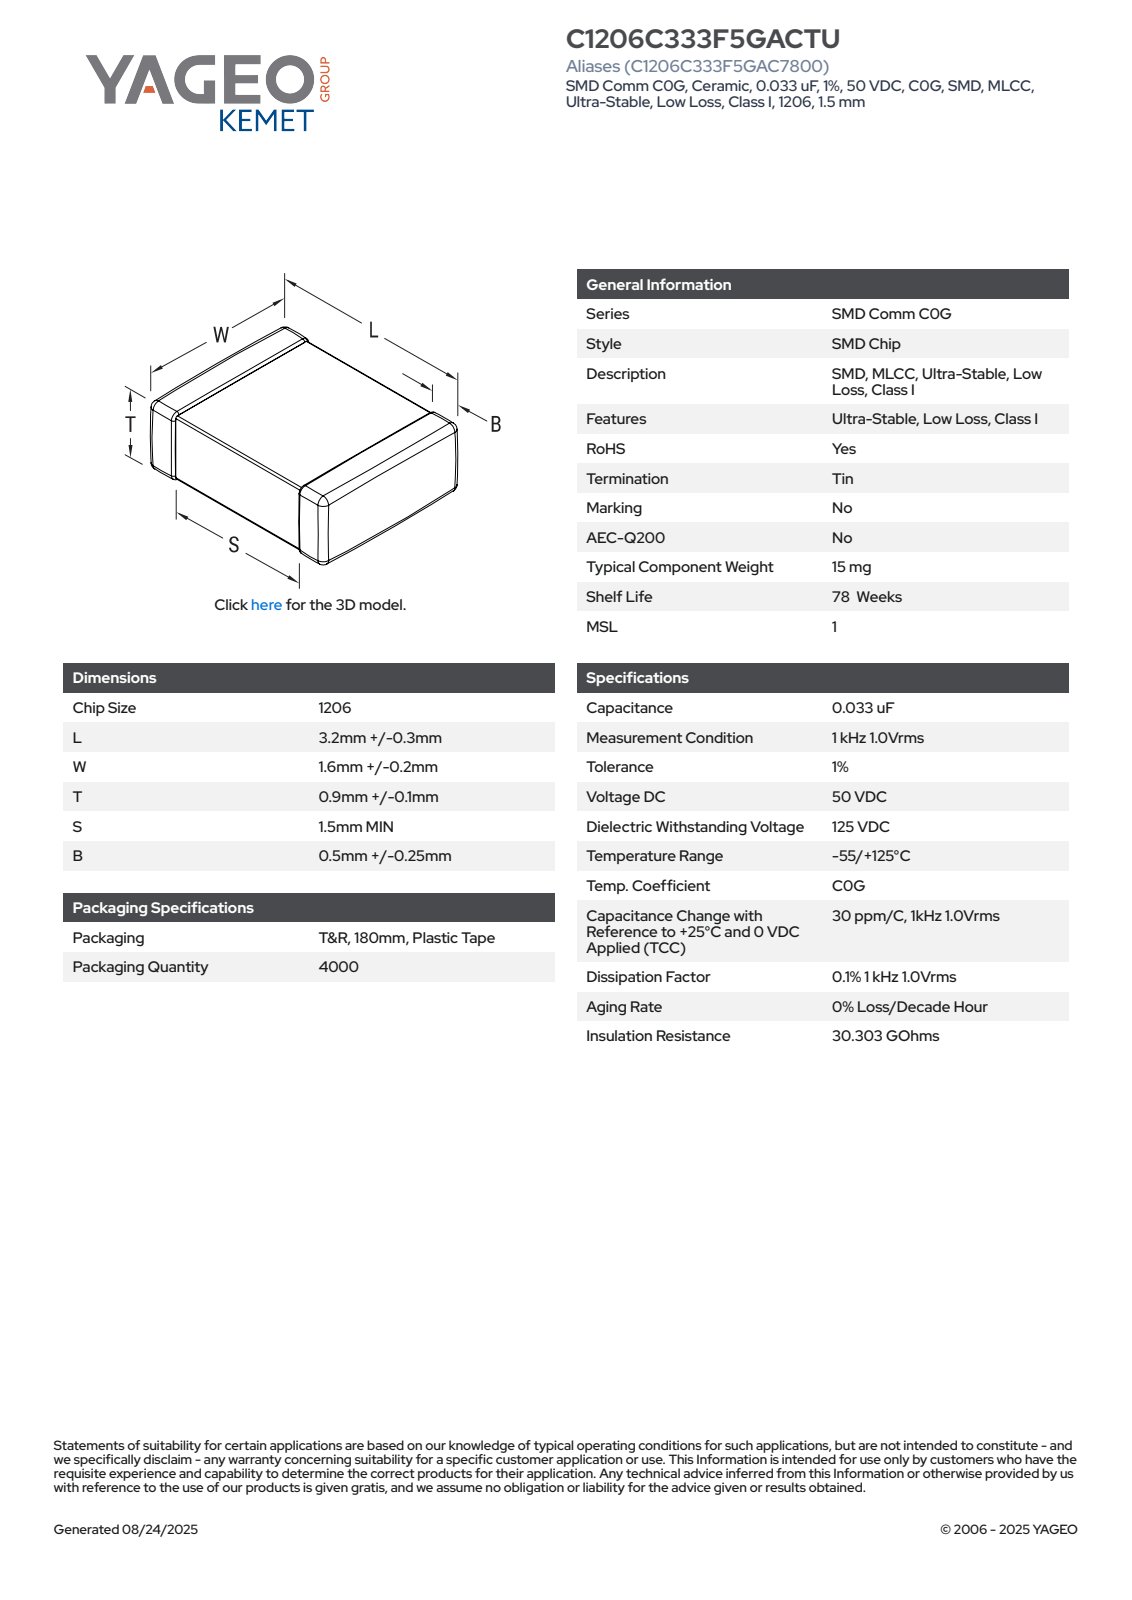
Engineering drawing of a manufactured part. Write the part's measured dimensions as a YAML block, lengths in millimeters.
part_name: "CCS_CCSTD_1206_L3.5W1.8T1B0.5"
step_written_by: "SolidWorks 2021 (AUTOMOTIVE_DESIGN)"
units: millimeters
bodies: {solids: 4, faces: 125, planar: 71, cylindrical: 38, other: 16}
overall_size: [3.5, 1.8, 1]
volume: 6
surface_area: 23
face_to_face_distances: [0.96, 0.92, 1.76, 1, 1.72, 3.5, 1.8, 0.97, 0.93, 1.63]
